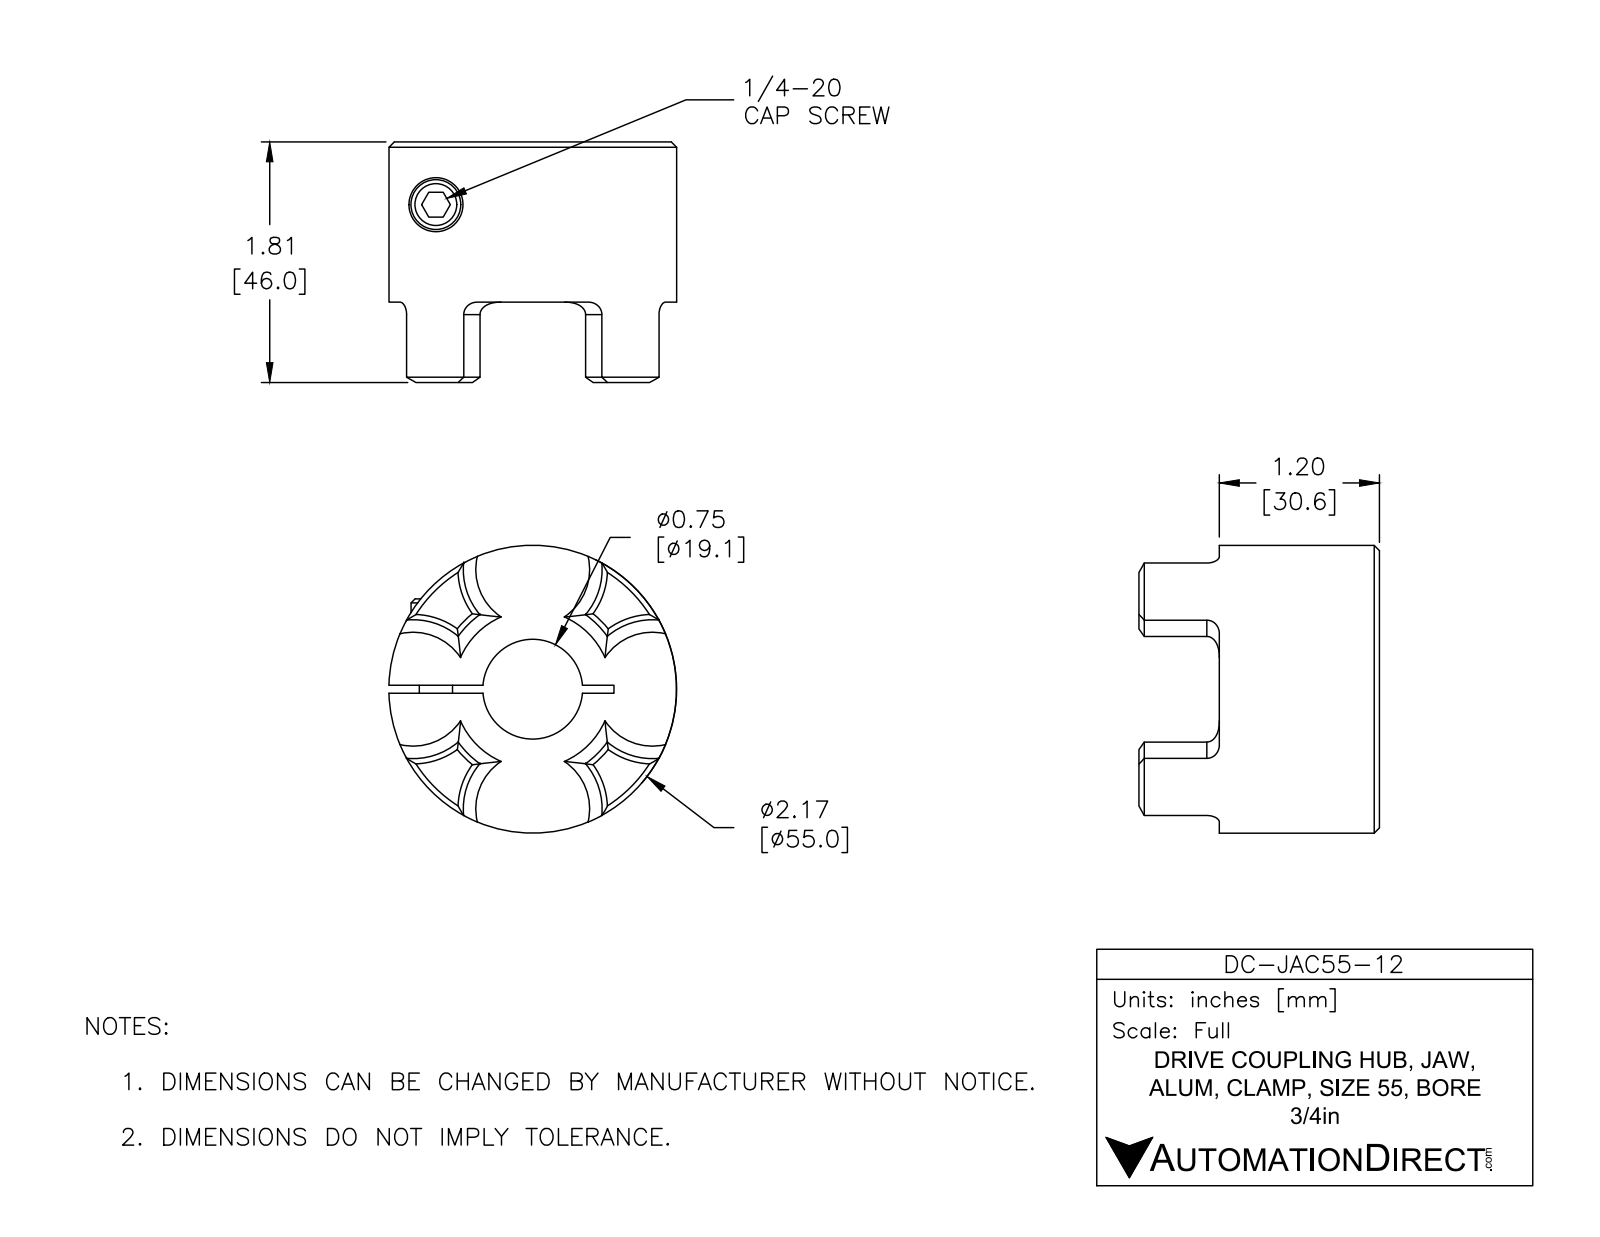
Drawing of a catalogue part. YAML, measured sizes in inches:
part_name: "DC-JA55-12_POST2016"
step_written_by: "SolidWorks 2016 (AUTOMOTIVE_DESIGN)"
units: inches
bodies: {solids: 2, faces: 92, planar: 22, cylindrical: 29, other: 41}
overall_size: [2.19, 2.165, 1.81]
volume: 4.131
surface_area: 25.41
round_holes:
  - {diameter: 0.266, count: 1}
  - {diameter: 0.406, count: 1}
  - {diameter: 0.75, count: 1}
round_bosses_or_shafts:
  - {diameter: 2.165, count: 1}
  - {diameter: 0.375, count: 1}
  - {diameter: 0.25, count: 1}
partial_cylinders:
  - {radius: 0.522, count: 4}
  - {radius: 0.687, count: 1}
face_to_face_distances: [1.205, 0.06, 1.81, 0.605, 0.46, 0.4, 0.187, 0.29, 0.35, 0.75]
